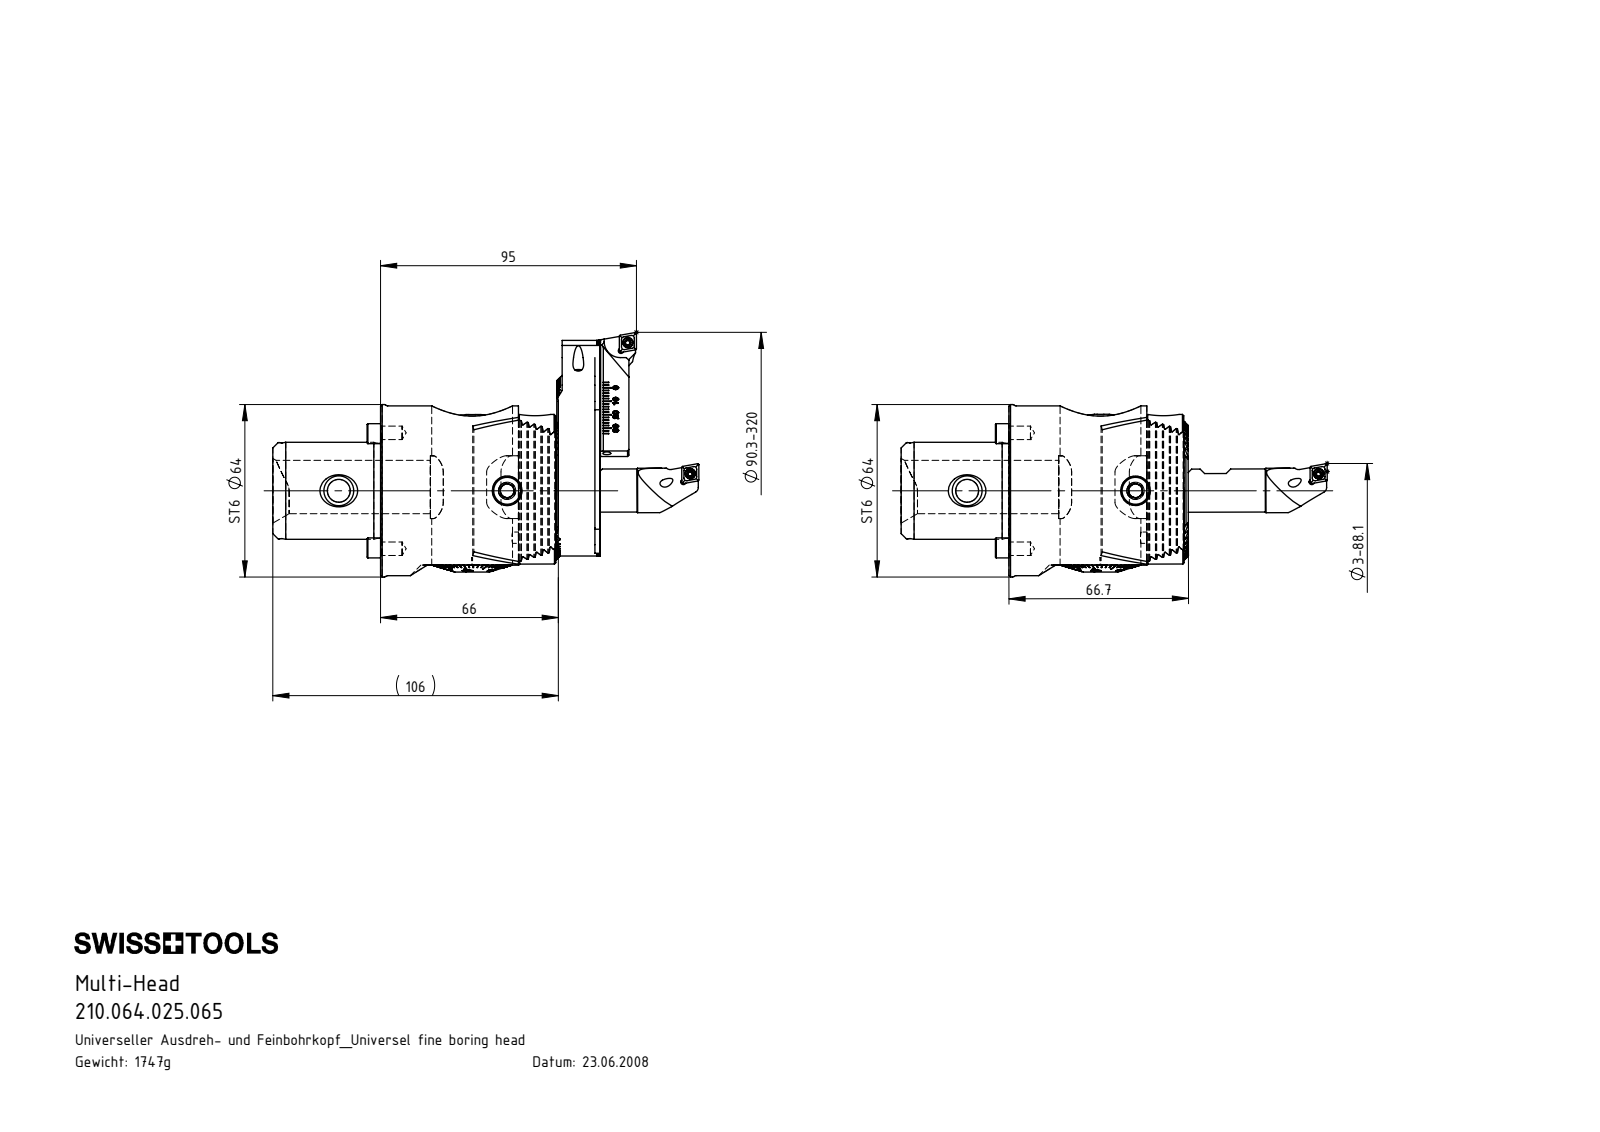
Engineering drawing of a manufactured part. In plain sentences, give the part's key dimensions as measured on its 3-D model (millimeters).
The part is named "WCA-ER2.001.006_A; ST6-MH1.K01.065; ST6-ER2.001.012_A; B20-WCA.K11.105_A (+4 more)". Its 3-D file was written by "SolidWorks 2015 (CONFIG_CONTROL_DESIGN)". It is 7 solids with 377 faces: 146 planar, 105 cylindrical and 126 other. Overall it measures 167.5 by 64 by 64 millimeters. Its volume is 162 418 cubic millimeters and its surface area 40 306 square millimeters. Round holes: 3 of diameter 5, 2 of diameter 3, 1 of diameter 2, 1 of diameter 2.05, 1 of diameter 2.8, 1 of diameter 3.85, 1 of diameter 4.2, 1 of diameter 6.4, 1 of diameter 8.5, 1 of diameter 11, 1 of diameter 30. Round bosses or shafts: 1 of diameter 64, 1 of diameter 63, 1 of diameter 36, 1 of diameter 35.8, 1 of diameter 35.3, 1 of diameter 16.5, 1 of diameter 16, 1 of diameter 8. Partial cylindrical surfaces (rounded edges, fillets, slot ends): 10 of radius 0.2, 6 of radius 0.21, 6 of radius 6, 5 of radius 0.36, 4 of radius 0.5, 2 of radius 5.47, 2 of radius 8.5, 2 of radius 18.05. The main face-to-face distances are 51.2, 2.38, 1.6, 4.76, 65, 13.8, 33.88, 2.39, 4.77, 7.14. The hole center spacings are 21.5, 3.89, 4, 4.1, 17.4, 38.9, 43, 62.5.
